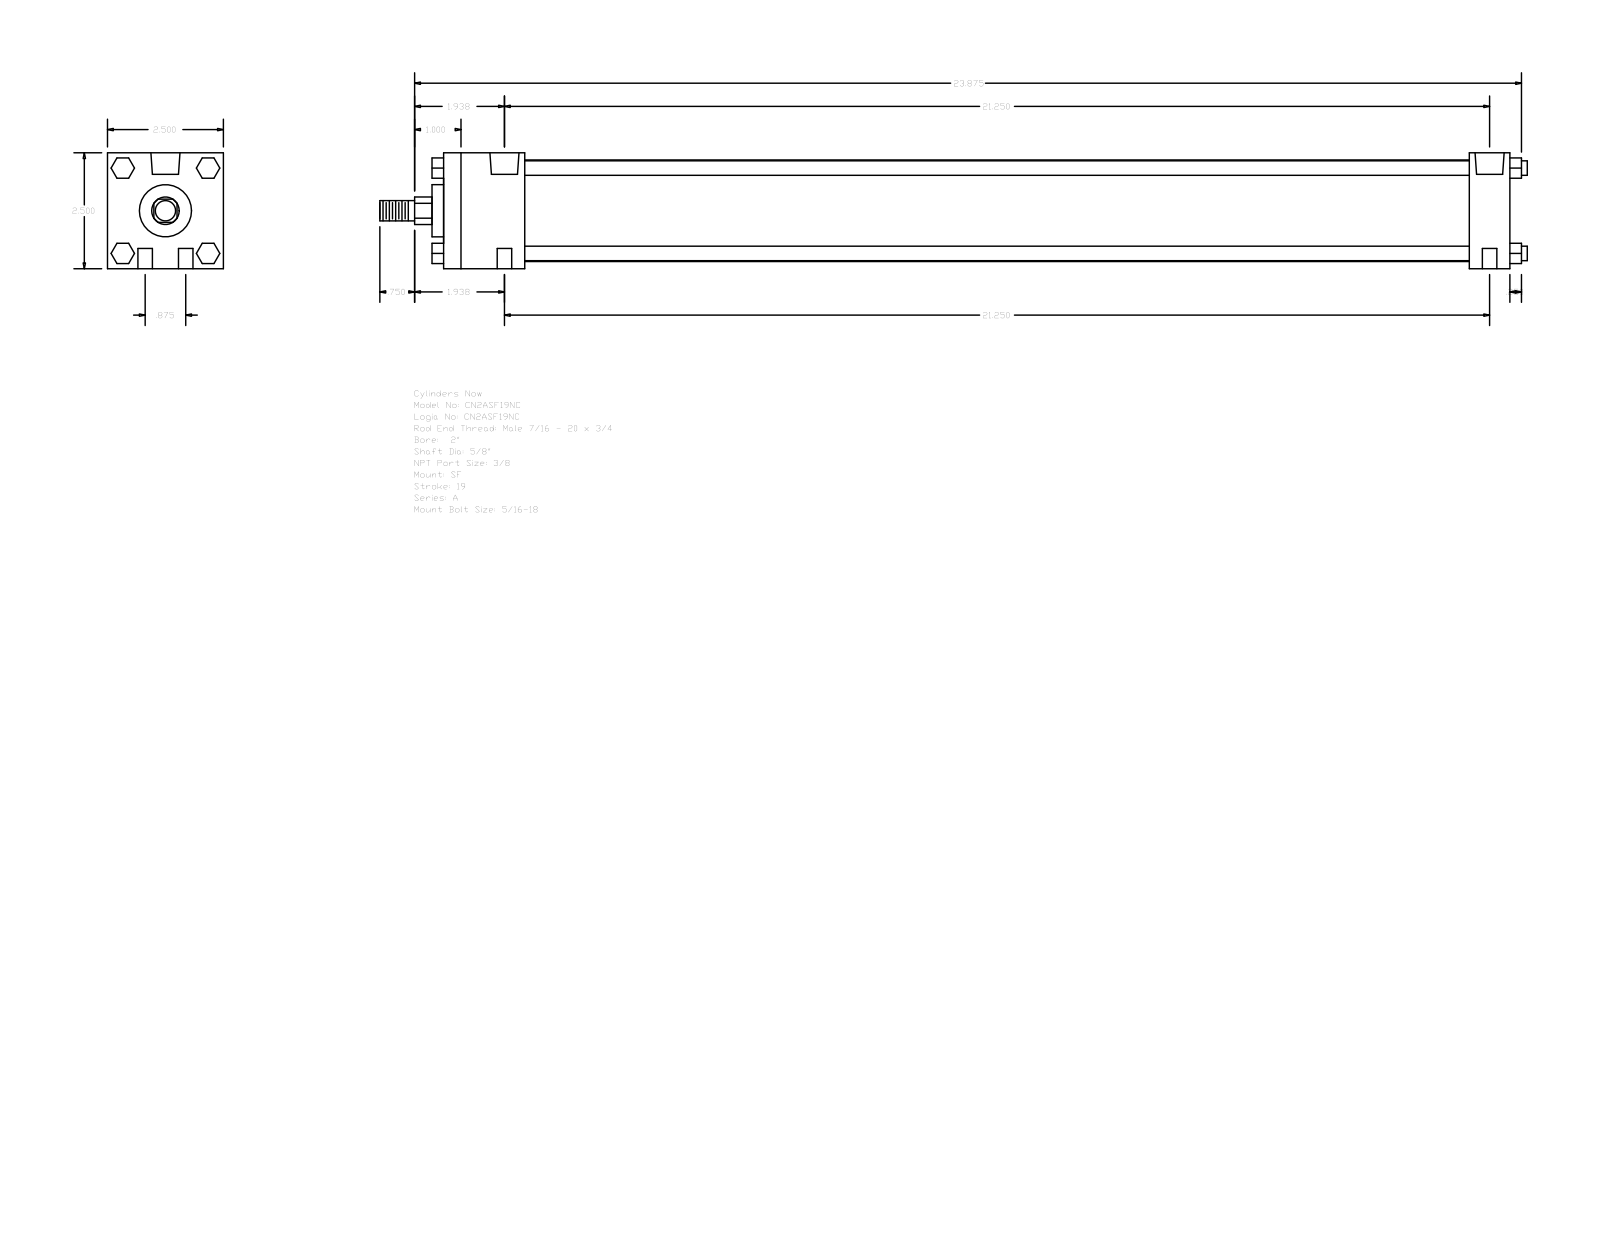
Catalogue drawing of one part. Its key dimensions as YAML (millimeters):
part_name: "A_SF__0200_0.625"
step_written_by: "GSSL Pune (CONFIG_CONTROL_DESIGN)"
units: millimeters
bodies: {solids: 0, faces: 124, planar: 94, cylindrical: 30, other: 0}
overall_size: [628.65, 63.5, 63.5]
round_holes:
  - {diameter: 7.94, count: 4}
  - {diameter: 5.56, count: 2}
  - {diameter: 15.93, count: 2}
round_bosses_or_shafts:
  - {diameter: 7.94, count: 4}
  - {diameter: 55.63, count: 1}
  - {diameter: 28.57, count: 1}
  - {diameter: 15.88, count: 1}
  - {diameter: 11.11, count: 1}
partial_cylinders:
  - {radius: 7.54, count: 1}
face_to_face_distances: [63.5, 584.2, 561.97, 22.23, 44.45, 517.52, 539.75, 50.8, 6.35, 568.32]
hole_center_spacings: [11.11, 539.86, 539.75, 22.22, 540.21, 531.8]
